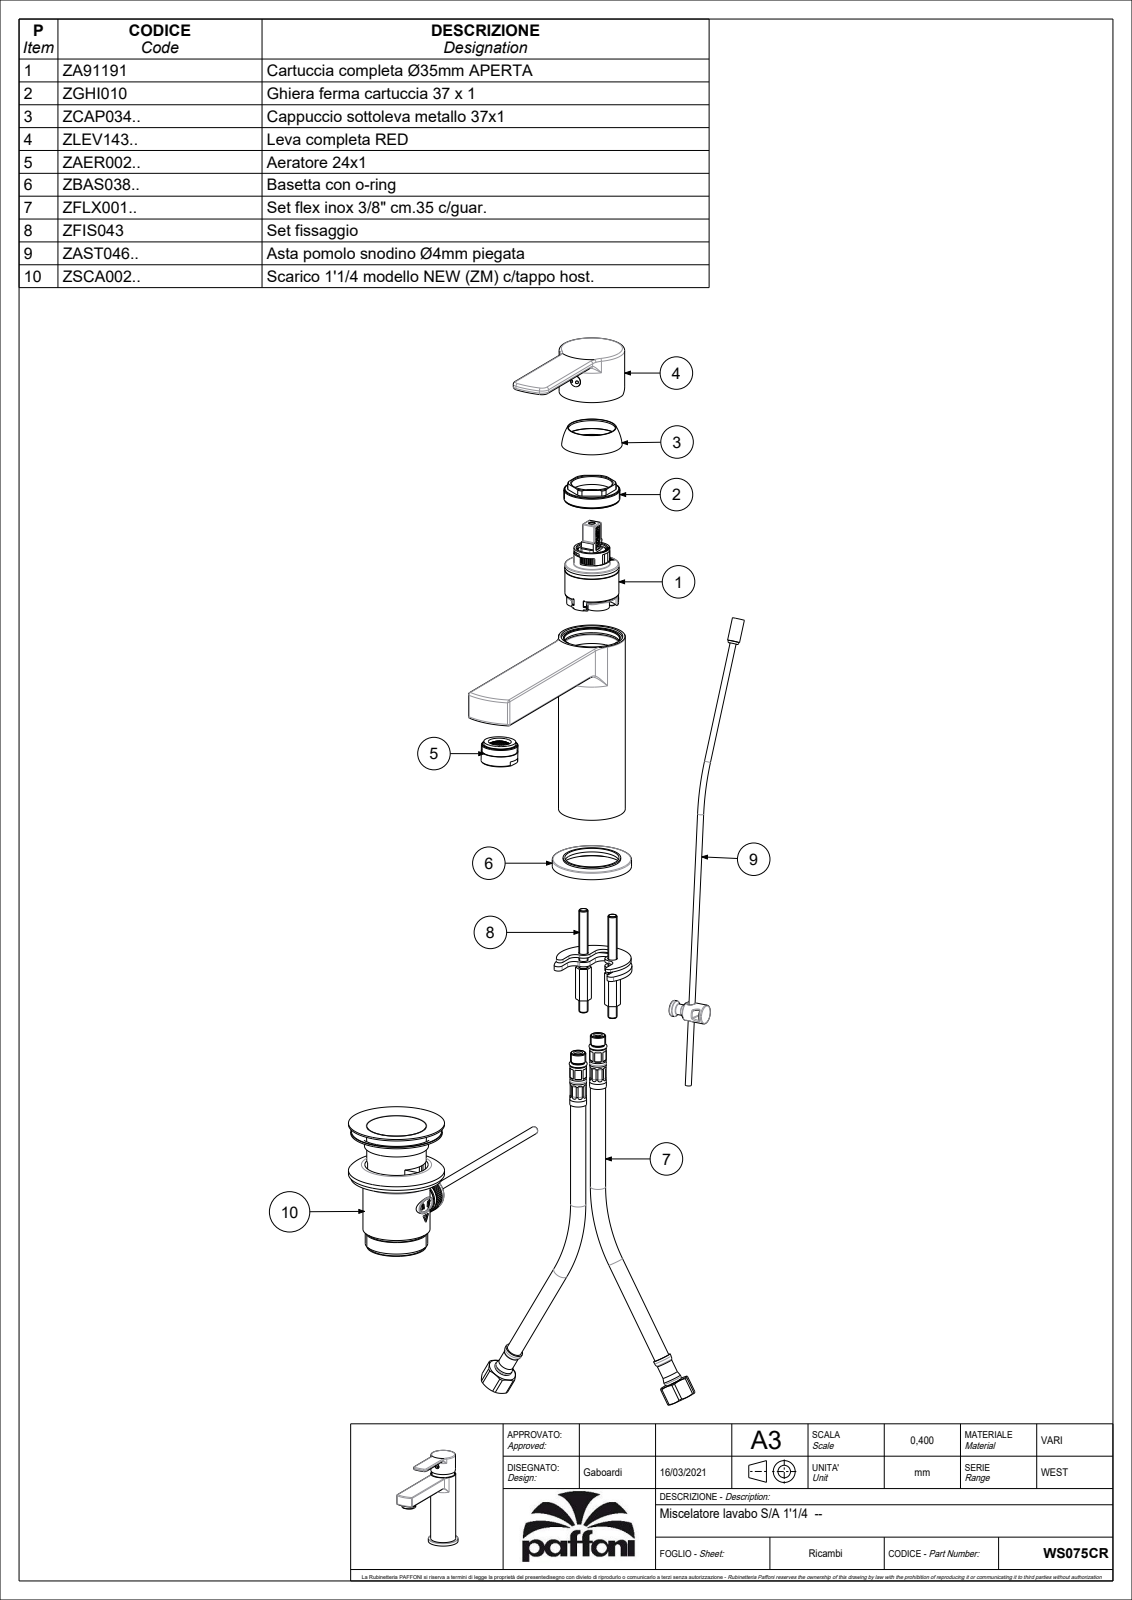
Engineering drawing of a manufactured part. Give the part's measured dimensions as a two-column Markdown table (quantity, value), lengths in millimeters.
| quantity | value |
| --- | --- |
| part name | WS075CR |
| STEP written by | CREO PARAMETRIC BY PTC INC, 2020044 (CONFIG_CONTROL_DESIGN) |
| units | millimeters |
| bodies | 4 solids, 3399 faces (2415 planar, 545 cylindrical, 439 other) |
| overall size | 181.89 × 162.55 × 52 |
| volume | 166 819 mm³ |
| surface area | 107 906 mm² |
| round holes (diameter × count) | 4.6 × 3, 5.5 × 3, 5 × 2, 7 × 2, 8 × 2, 9 × 2, 11 × 2, 3 × 1, 3.4 × 1, 3.5 × 1, 4 × 1, 4.5 × 1 |
| round bosses / shafts (diameter × count) | 10.8 × 2, 8.2 × 2, 6 × 2, 4.8 × 2, 4 × 2, 52 × 1, 43 × 1, 42.8 × 1 |
| partial cylindrical surfaces (radius × count) | 0.5 × 87, 1.5 × 22, 1 × 17, 2 × 9, 1.7 × 6, 0.8 × 4, 5 × 4, 5.8 × 4 |
| main face-to-face distances | 3, 14, 17, 36.05, 53.05, 15, 27, 4.5, 1, 48.55 |
| hole center spacings | 13.6, 0.5, 2.83, 8.6, 9.01, 13.45, 13.46, 14.5 |
